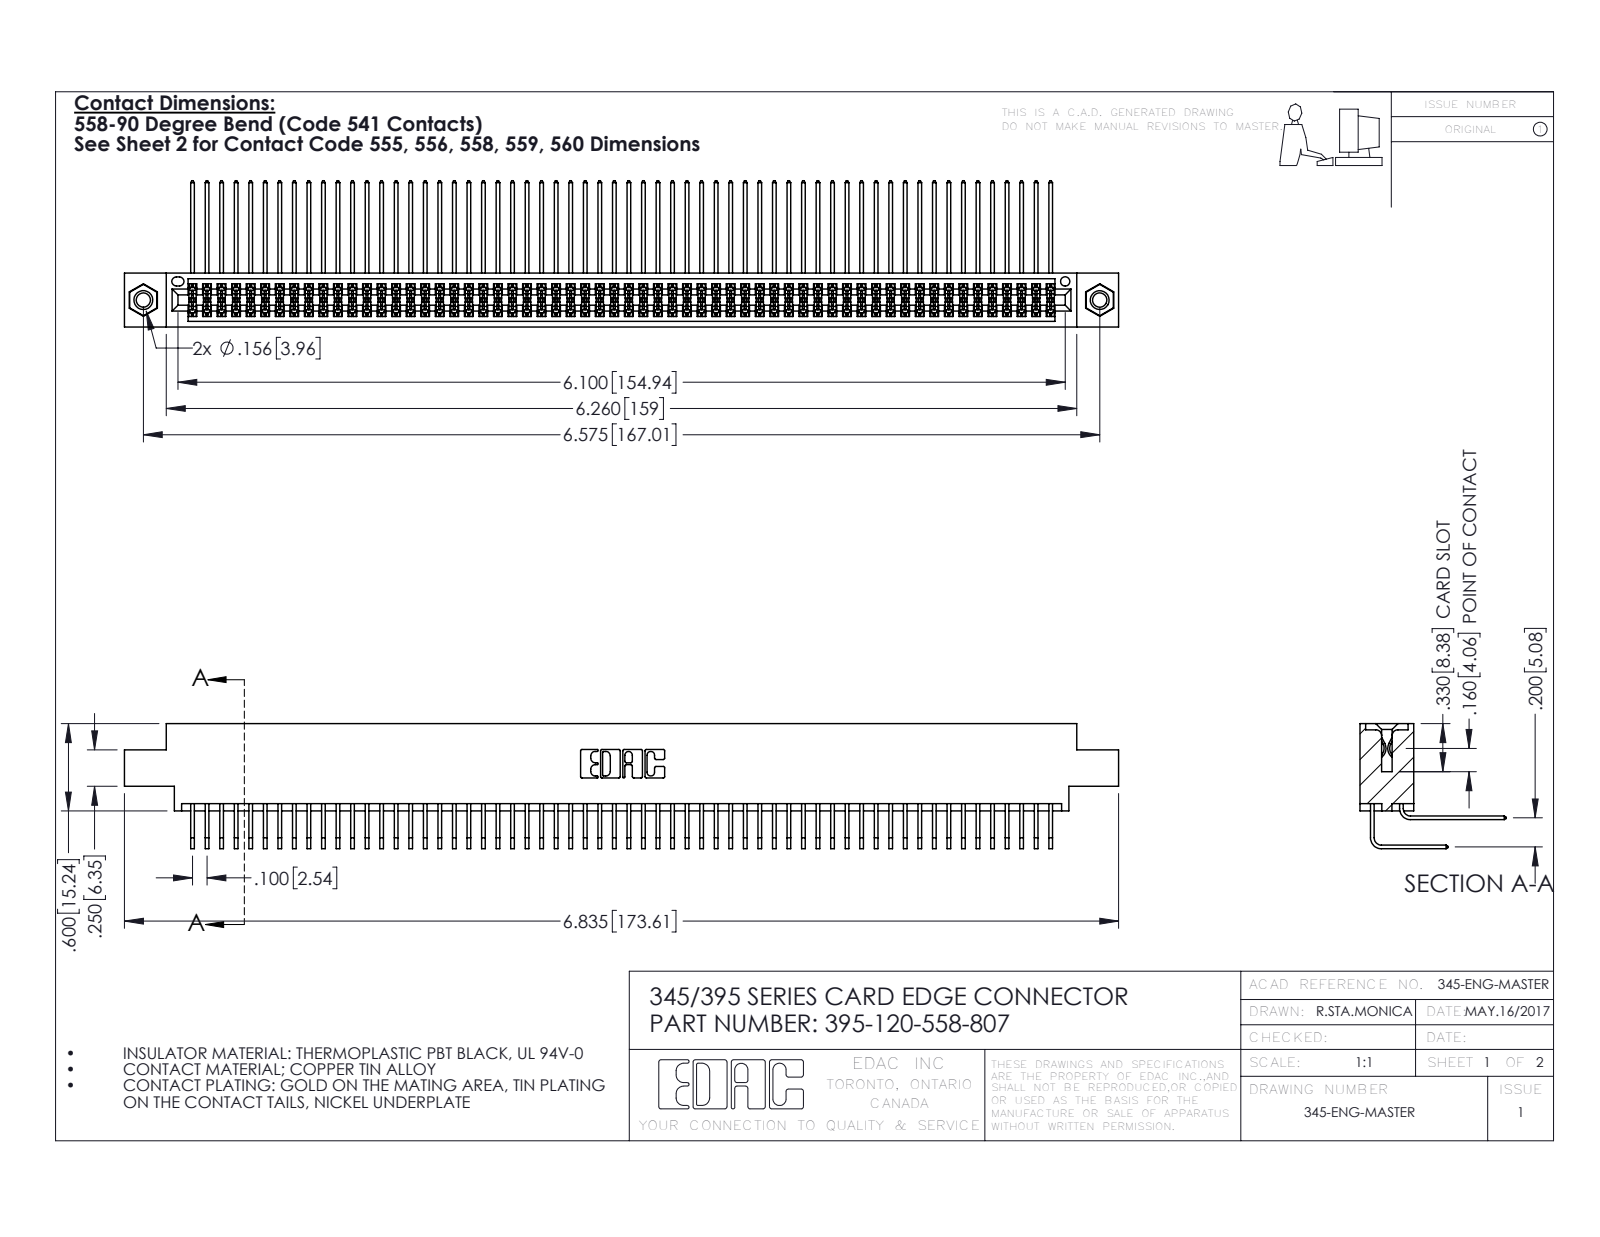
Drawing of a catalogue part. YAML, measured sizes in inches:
part_name: "345-250-001_345-250-005-103; 345-292-001_558 559 Tail - 1; 395-120-558-807; 345-292-001_558 Tail - 2 (+1 more)"
step_written_by: "SolidWorks 2016 (CONFIG_CONTROL_DESIGN)"
units: inches
bodies: {solids: 123, faces: 6430, planar: 4316, cylindrical: 2098, other: 16}
overall_size: [6.835, 1.005, 0.859]
volume: 1.074
surface_area: 46.17
round_holes:
  - {diameter: 0.098, count: 2}
  - {diameter: 0.125, count: 2}
  - {diameter: 0.156, count: 2}
  - {diameter: 0.064, count: 1}
round_bosses_or_shafts:
  - {diameter: 0.155, count: 2}
partial_cylinders:
  - {radius: 0.006, count: 181}
  - {radius: 0.01, count: 22}
  - {radius: 0.007, count: 6}
  - {radius: 0.031, count: 6}
  - {radius: 0.026, count: 3}
  - {radius: 0.014, count: 2}
  - {radius: 0.019, count: 2}
  - {radius: 0.022, count: 2}
face_to_face_distances: [0.072, 0.298, 0.2, 0.37, 0.098, 0.272, 0.025, 0.225, 0.175, 0.025]
hole_center_spacings: [0.27, 6.339, 6.575]
